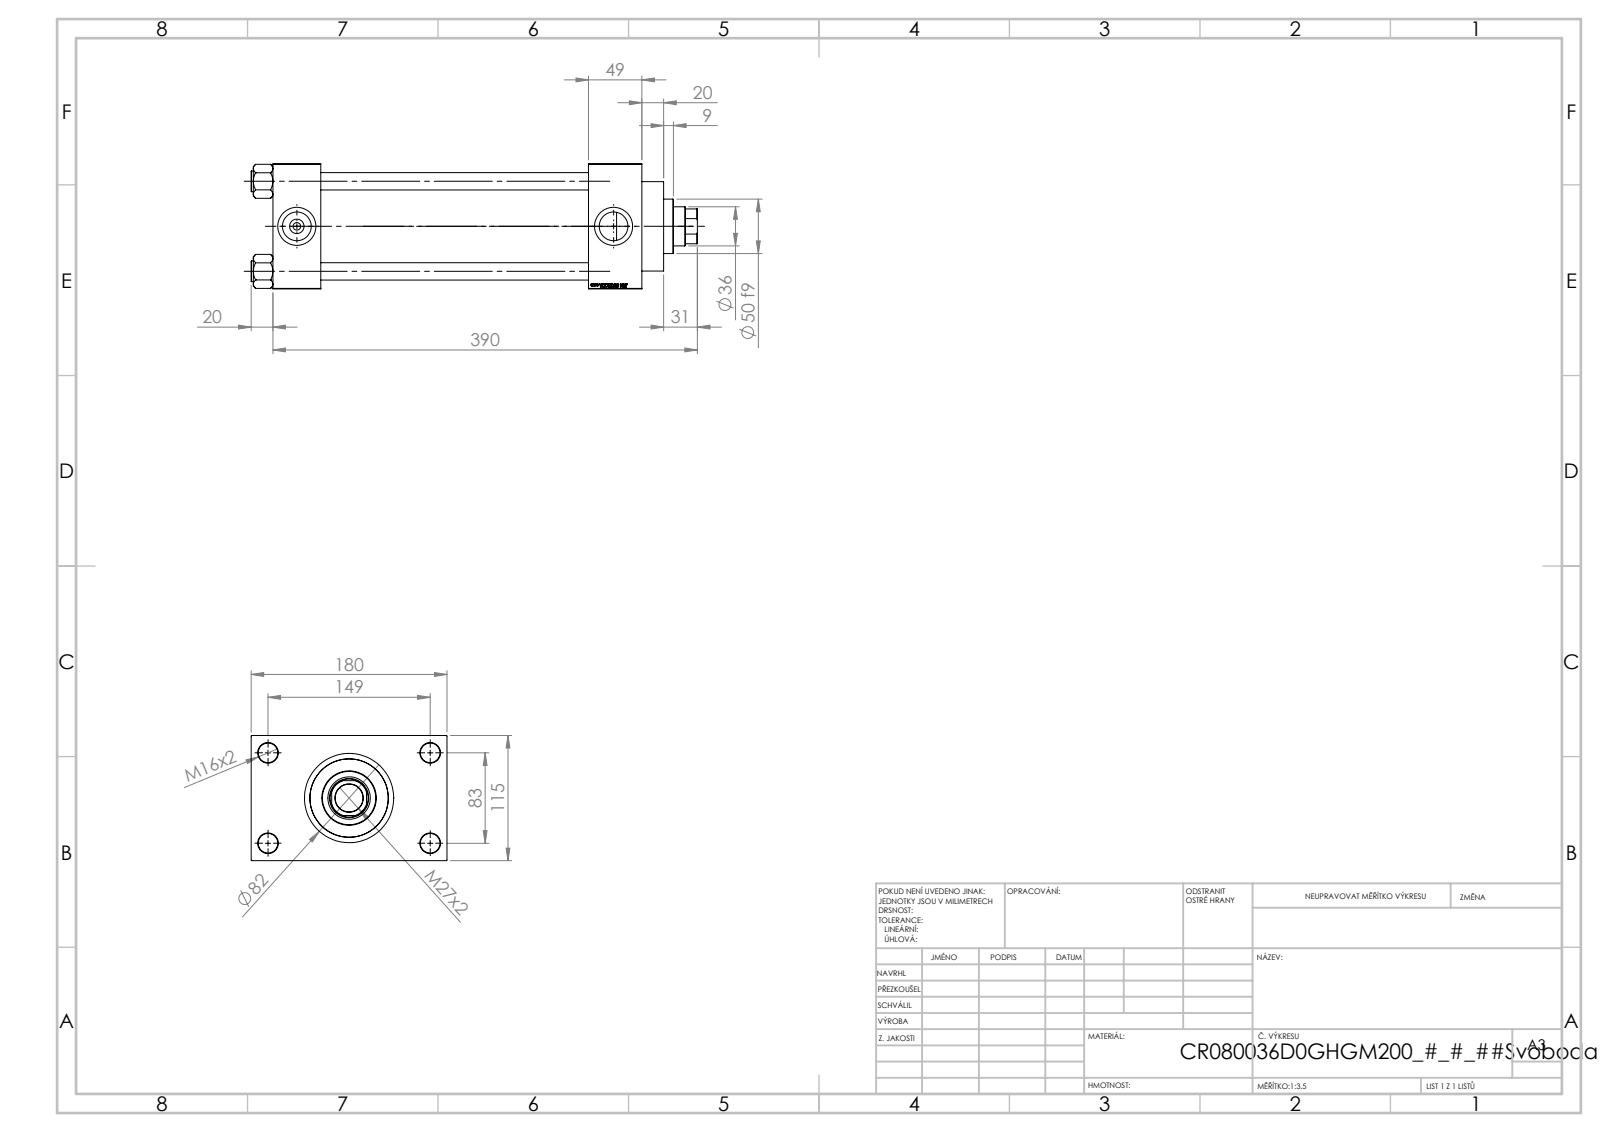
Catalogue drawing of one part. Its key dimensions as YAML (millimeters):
part_name: "V215CR_VCP_D; V215CR_D_Body; NUT_M5_D; V215CR_D_TYCINKA (+1 more)"
step_written_by: "SolidWorks 2019 (CONFIG_CONTROL_DESIGN)"
units: millimeters
bodies: {solids: 11, faces: 1151, planar: 545, cylindrical: 88, other: 518}
overall_size: [410, 180, 115]
volume: 2448000
surface_area: 447014
round_holes:
  - {diameter: 16, count: 4}
  - {diameter: 18, count: 4}
  - {diameter: 7, count: 2}
  - {diameter: 26.44, count: 2}
  - {diameter: 35, count: 2}
  - {diameter: 25.5, count: 1}
  - {diameter: 36, count: 1}
  - {diameter: 39, count: 1}
  - {diameter: 61, count: 1}
  - {diameter: 72, count: 1}
  - {diameter: 80, count: 1}
round_bosses_or_shafts:
  - {diameter: 19, count: 4}
  - {diameter: 86, count: 1}
  - {diameter: 82, count: 1}
  - {diameter: 50, count: 1}
partial_cylinders:
  - {radius: 17.5, count: 1}
face_to_face_distances: [115, 246, 295, 49, 44, 290, 339, 32.5, 147.5, 180]
hole_center_spacings: [33.15, 58.48, 82.7, 85.28, 89.24, 115.85, 142.43, 83]
